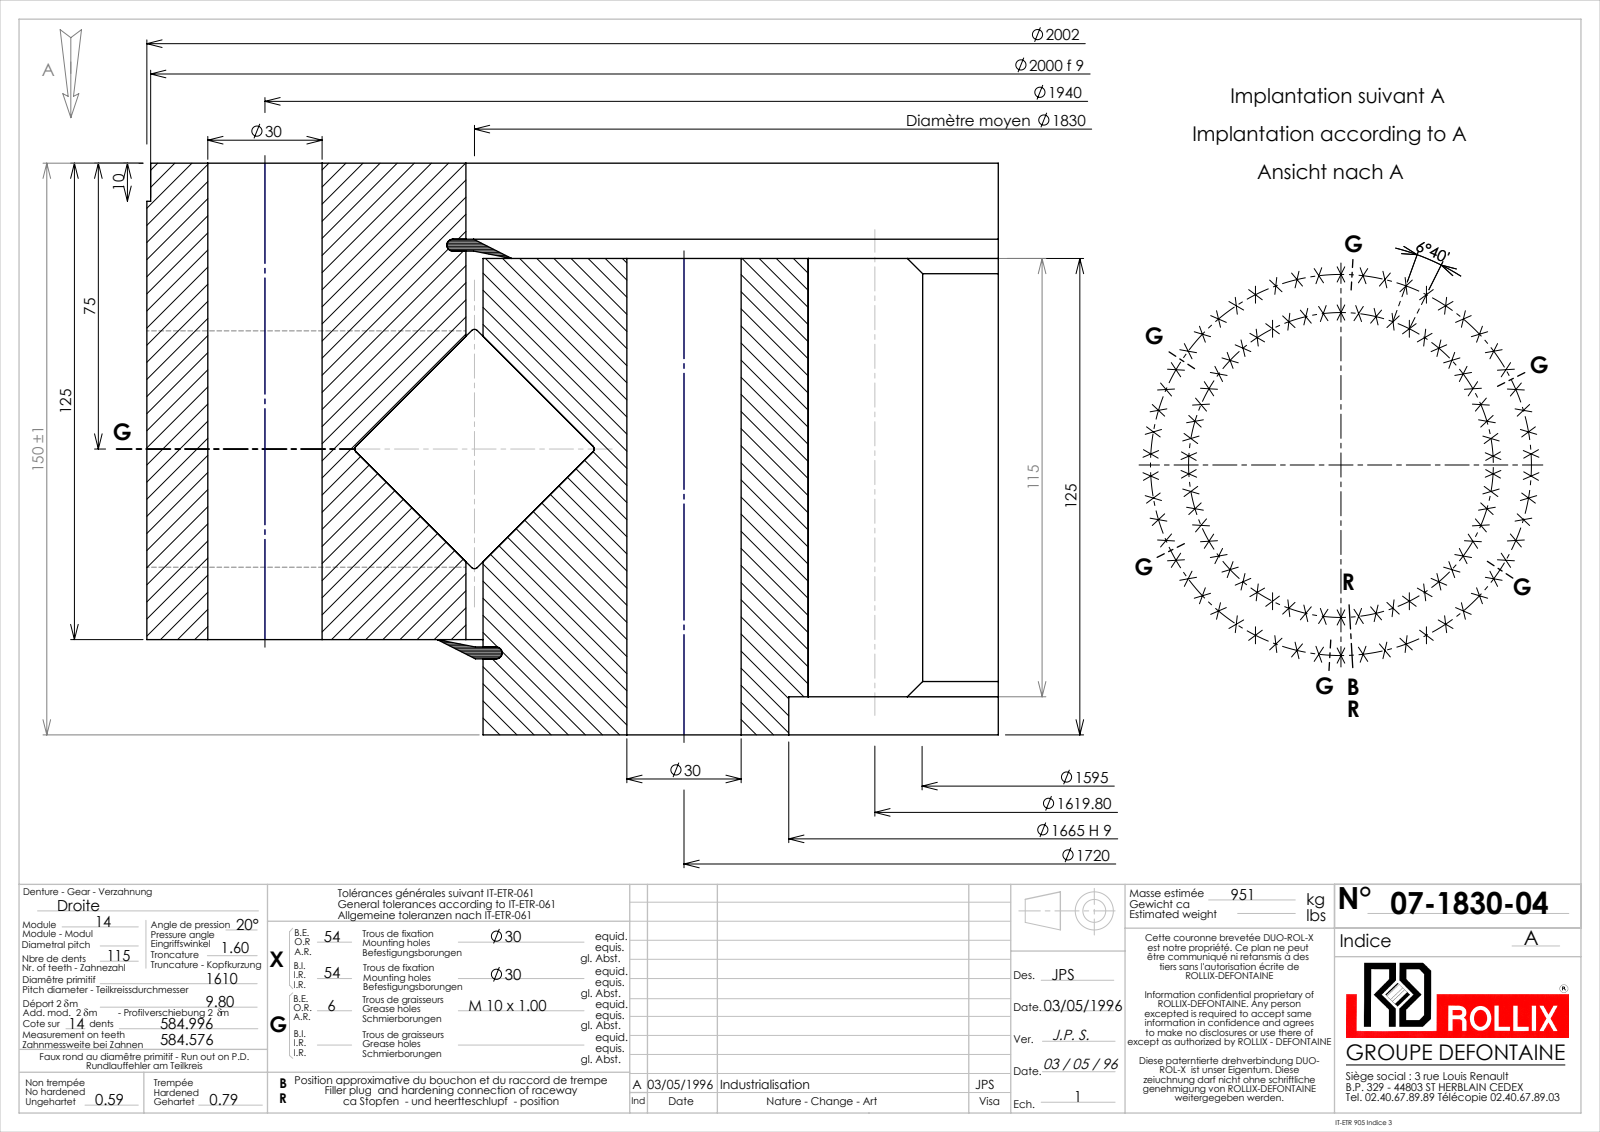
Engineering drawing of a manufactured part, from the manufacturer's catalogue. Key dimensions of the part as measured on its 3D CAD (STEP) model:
Part name (STEP PRODUCT): 07-1830-04
STEP written by: SolidWorks 2016 (CONFIG_CONTROL_DESIGN)
Units: millimetres
Bodies: 5 solids, 999 faces (246 planar, 479 cylindrical, 274 other)
Overall size (bounding box): 2002 × 2002 × 150
Volume: 111 300 000 mm³ · Surface area: 7 448 000 mm²
Round holes (diameter × count): ⌀30 ×108, ⌀9 ×6, ⌀1665 ×1, ⌀1834.5 ×1
Round bosses / shafts (diameter × count): ⌀2002 ×1, ⌀2000 ×1, ⌀1825.5 ×1, ⌀45 ×1
Partial cylindrical surfaces — rounded edges, fillets, slot ends (radius × count): R797.5 ×1, R827.4 ×1
Main face-to-face distances: 25, 125, 100, 150, 10, 140, 15, 115, 19.95, 130.05
Hole centre spacings: 860, 199.68, 100.01, 396.66, 493.3, 681.26, 771.94, 298.68
